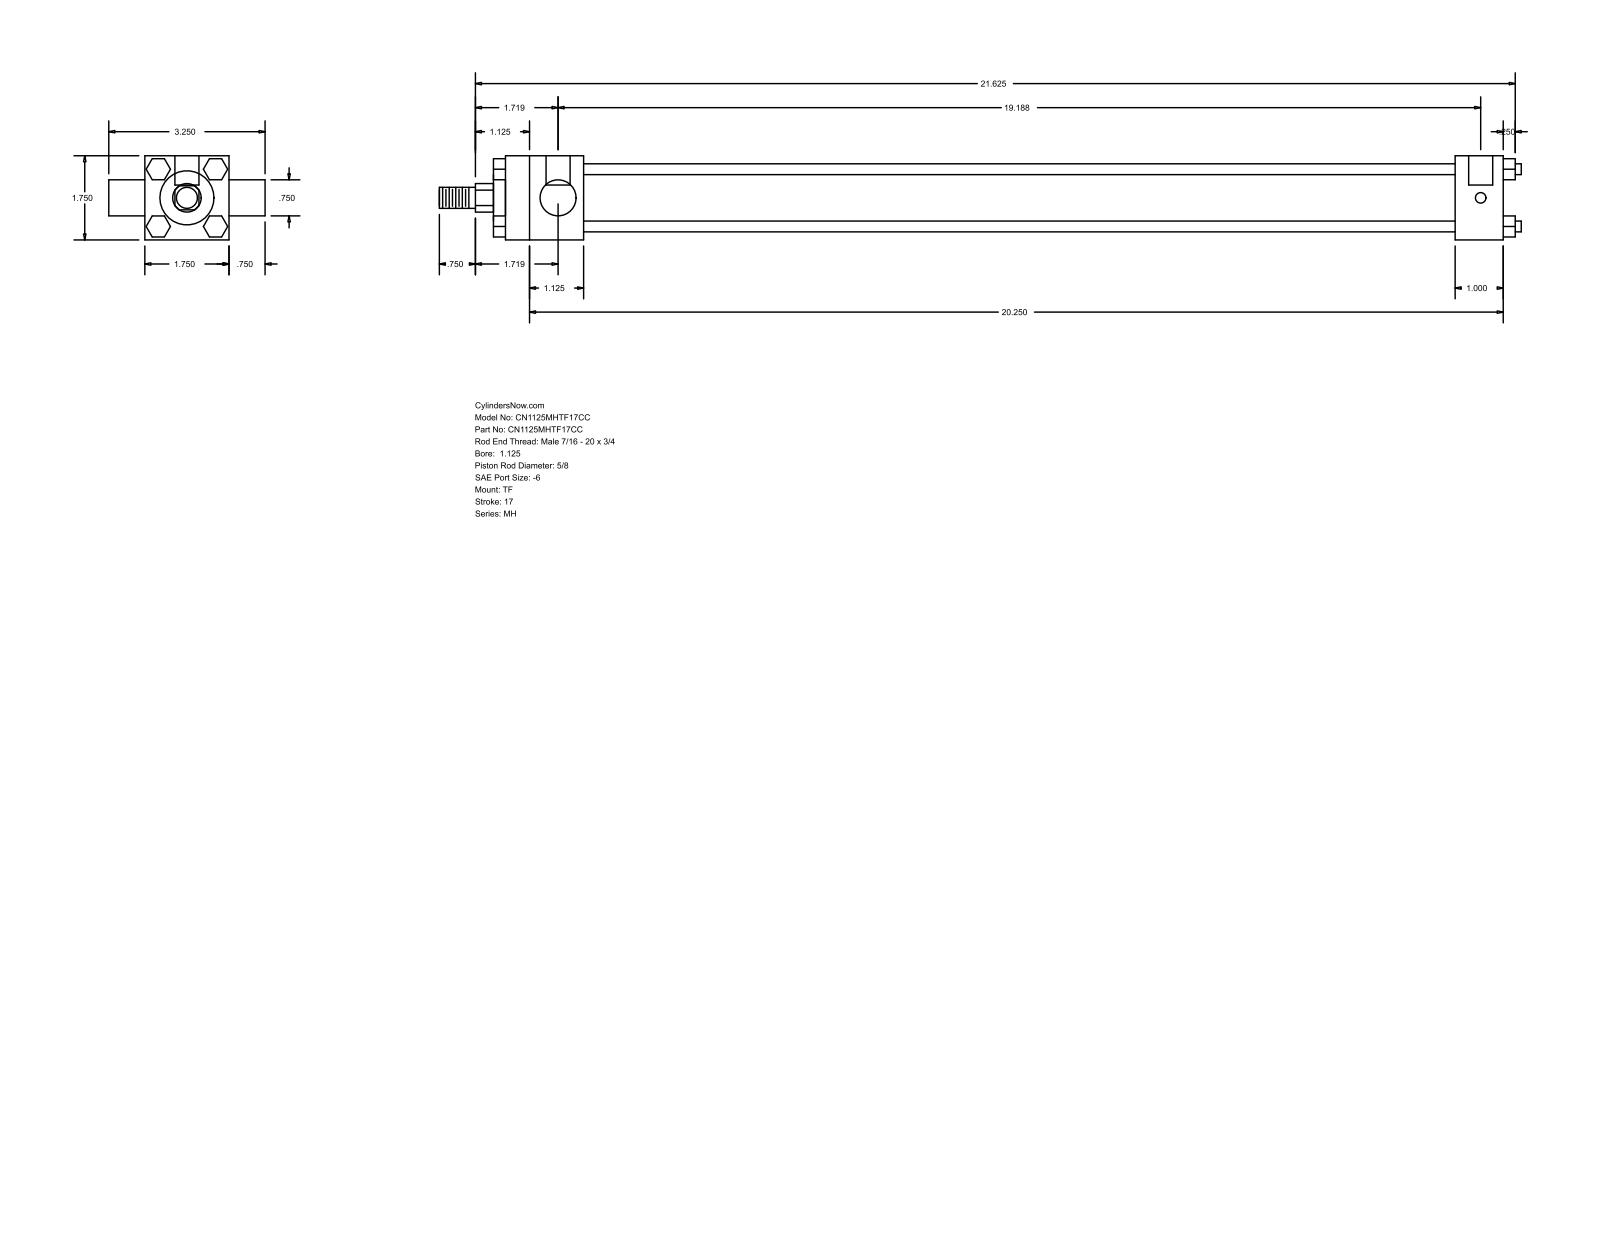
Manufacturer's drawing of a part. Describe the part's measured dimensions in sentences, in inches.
The part is named "MH_TF__0112_0.625". Its 3-D file was written by "GSSL Pune (CONFIG_CONTROL_DESIGN)". It is 0 solids with 120 faces: 92 planar, 28 cylindrical and 0 other. Overall it measures 22.5 by 3.25 by 1.75 inches. Round holes: 3 of diameter 0.219, 2 of diameter 0.5. Round bosses or shafts: 4 of diameter 0.225, 1 of diameter 1.375, 1 of diameter 1.125, 1 of diameter 0.75, 1 of diameter 0.625, 1 of diameter 0.437. Partial cylindrical surfaces (rounded edges, fillets, slot ends): 1 of radius 0.297. The main face-to-face distances are 1.75, 0.25, 21, 0.437, 1, 18.125, 19.125, 1.625, 19.75, 20.75. The hole center spacings are 0.125, 19.063, 19.187.
